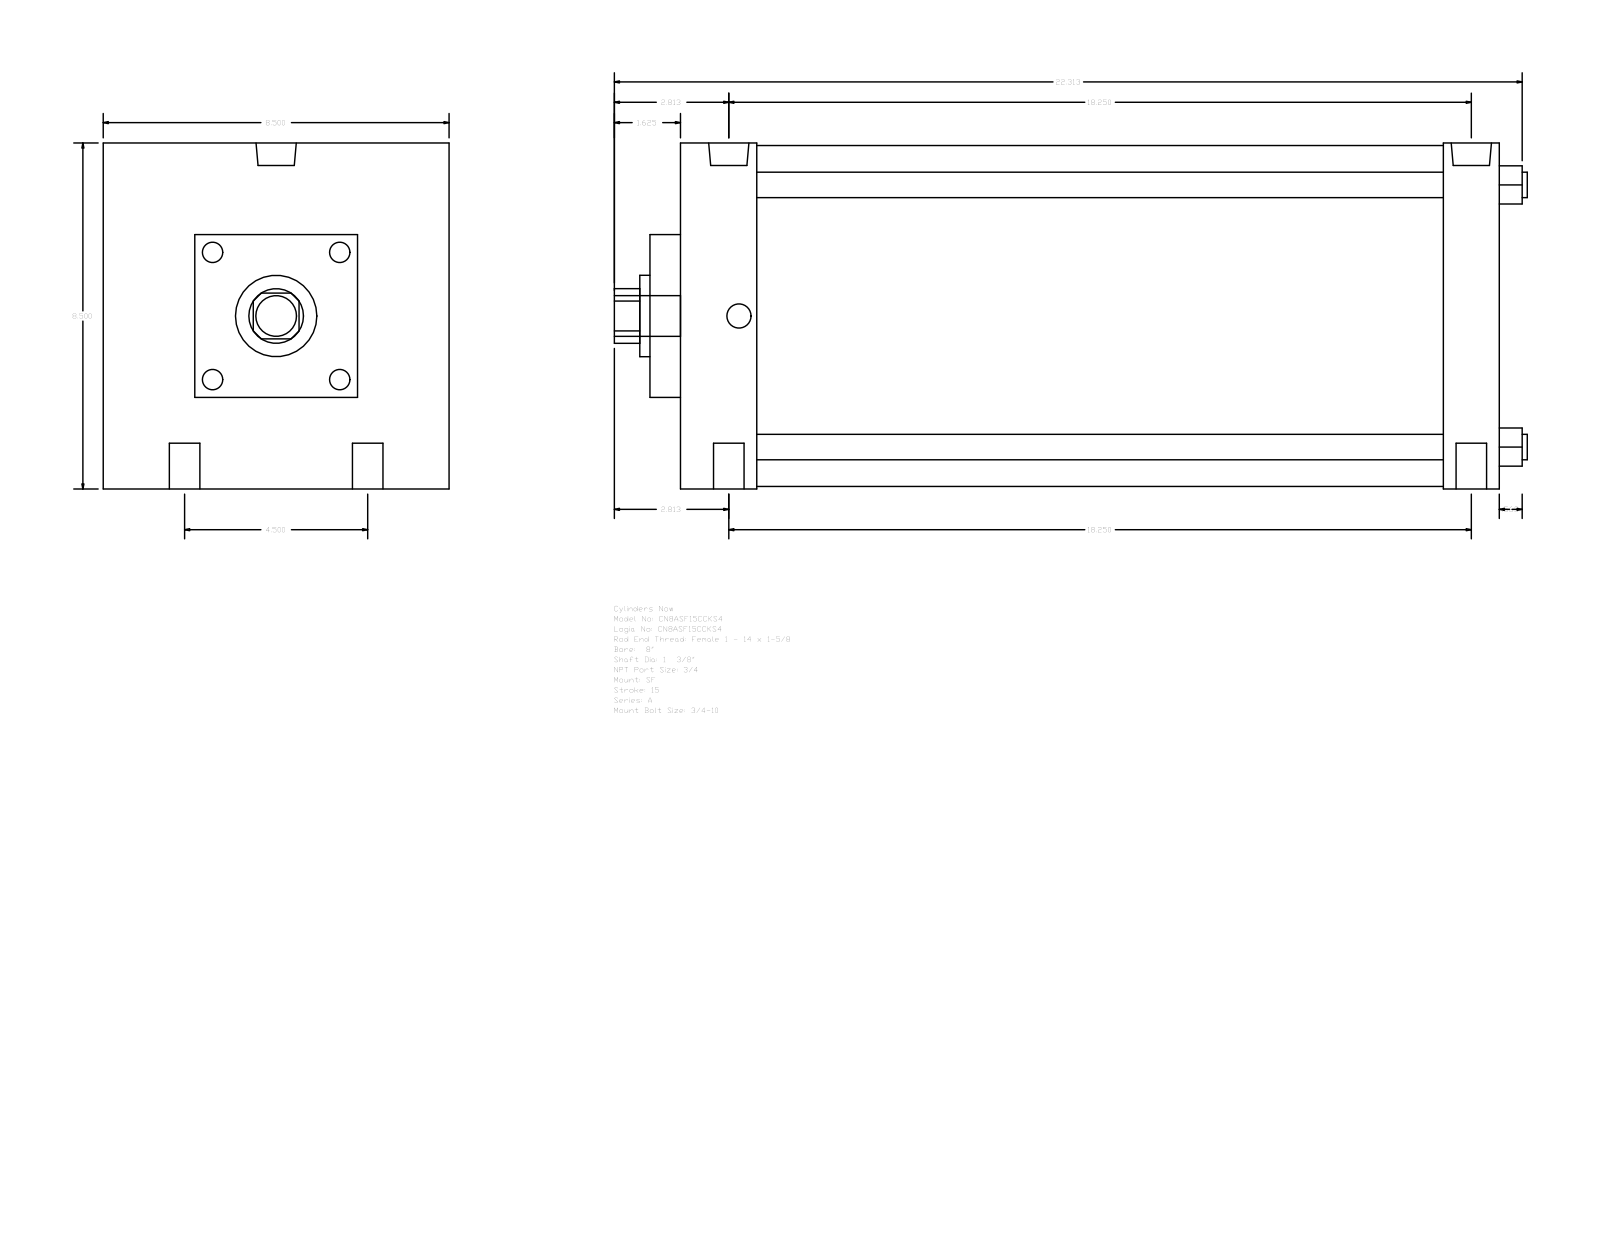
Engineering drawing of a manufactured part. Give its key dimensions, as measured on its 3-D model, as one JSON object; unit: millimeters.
{"part_name": "A_SF__0800_1.375", "step_written_by": "GSSL Pune (CONFIG_CONTROL_DESIGN)", "units": "millimeters", "bodies": {"solids": 0, "faces": 93, "planar": 67, "cylindrical": 26, "other": 0}, "overall_size": [569.91, 215.9, 215.9], "round_holes": [[19.05, 4], [15.08, 2], [25.12, 2], [34.92, 1], [50.8, 1]], "round_bosses_or_shafts": [[15.88, 4], [212.72, 1], [25.4, 1]], "partial_cylinders_radius": [[17.06, 1]], "face_to_face_distances": [511.18, 215.9, 47.63, 476.25, 428.62, 463.55, 34.93, 19.04, 66.67, 495.29], "hole_center_spacings": [57.15, 467.06, 463.55, 114.3, 477.43, 450.85]}
